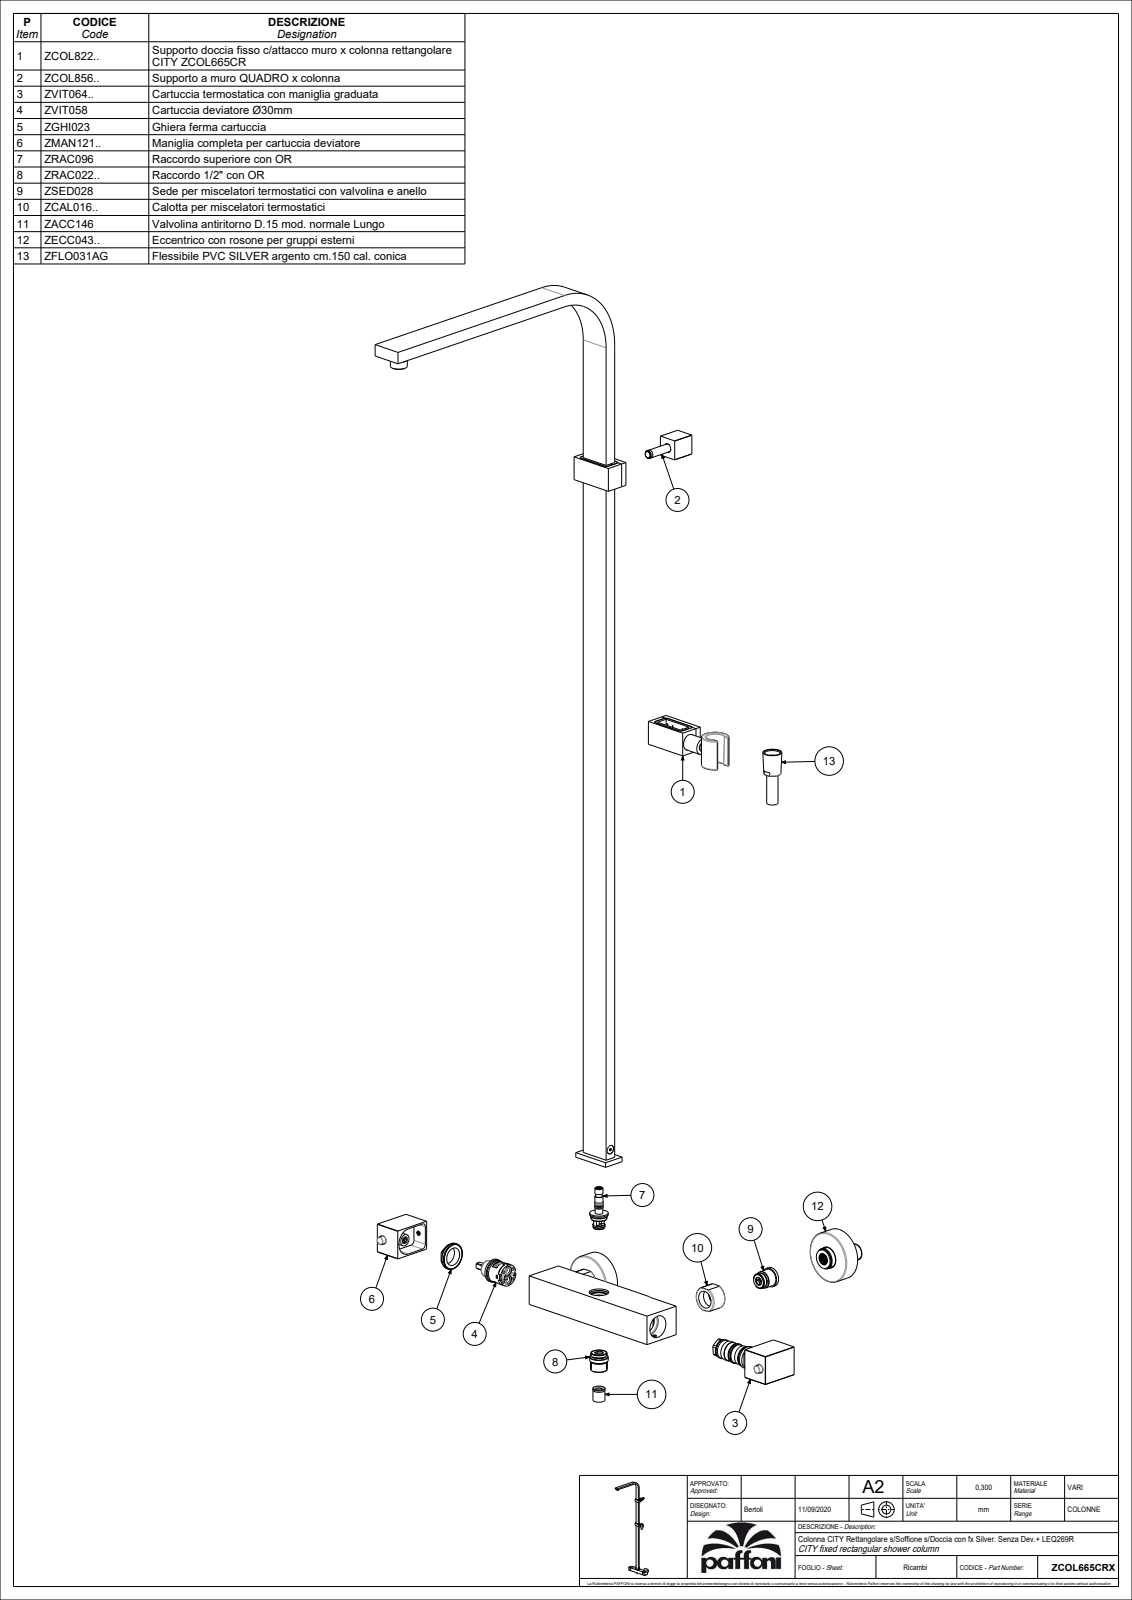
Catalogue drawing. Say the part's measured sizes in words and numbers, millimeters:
The part is named "ZCOL665CRX". Its 3-D file was written by "CREO PARAMETRIC BY PTC INC, 2020044 (CONFIG_CONTROL_DESIGN)". It is 12 solids with 3037 faces: 2088 planar, 581 cylindrical and 368 other. Overall it measures 1215.5 by 446.9 by 279.05 millimeters. Its volume is 651 715 cubic millimeters and its surface area 535 132 square millimeters. Round holes: 10 of diameter 5.5, 8 of diameter 4.5, 4 of diameter 6, 3 of diameter 3.3, 3 of diameter 10, 3 of diameter 15, 3 of diameter 20.2, 2 of diameter 2.5, 2 of diameter 3, 2 of diameter 3.25, 2 of diameter 4, 2 of diameter 4.2. Round bosses or shafts: 8 of diameter 5, 2 of diameter 63.5, 2 of diameter 27, 2 of diameter 24, 2 of diameter 23, 2 of diameter 20, 2 of diameter 14.5, 2 of diameter 11. Partial cylindrical surfaces (rounded edges, fillets, slot ends): 84 of radius 1, 18 of radius 4, 16 of radius 0.5, 10 of radius 5, 2 of radius 1.75, 2 of radius 15.6, 1 of radius 2.25, 1 of radius 5.15. The main face-to-face distances are 1.5, 13.5, 15, 12, 38.5, 40, 37, 37.5, 11.5, 2.75. The hole center spacings are 17.03, 40.52, 315, 22, 28.23, 52, 56.46, 304.28.
